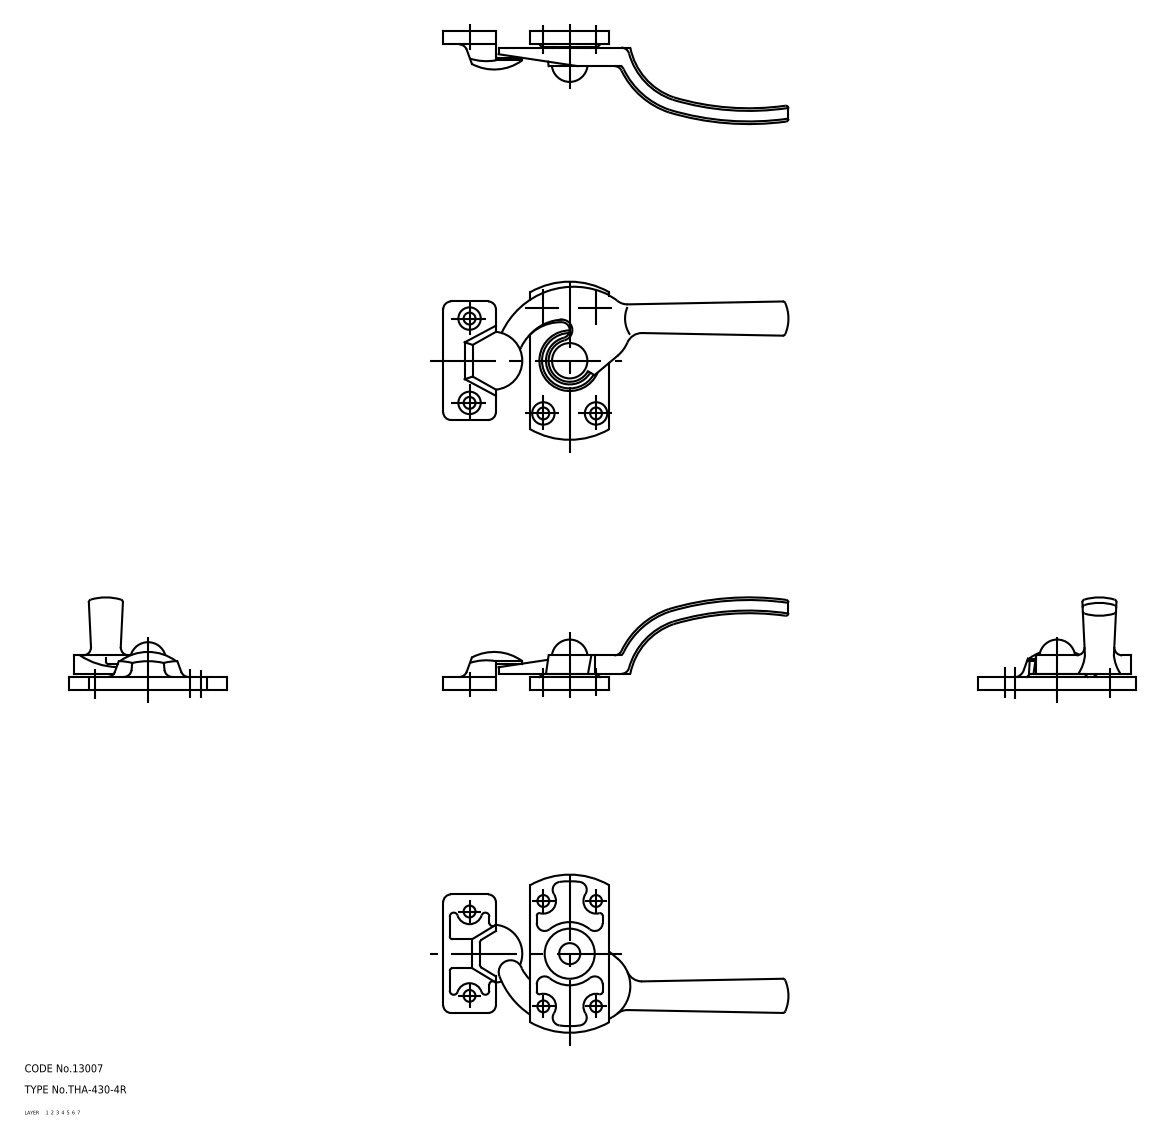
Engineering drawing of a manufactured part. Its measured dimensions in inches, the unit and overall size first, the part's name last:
Units: inches
Overall size (bounding box): 5.157 × 2.362 × 1.386
Volume: 1.364 in³ · Surface area: 22.95 in²
Bodies: 6 solids, 161 faces (0 planar, 0 cylindrical, 161 other)
Part name (STEP PRODUCT): washer_C_mr; washer_B_mr; rivet_mr; keeper_mr (+3 more)
STEP written by: CADfix (AUTOMOTIVE_DESIGN)
